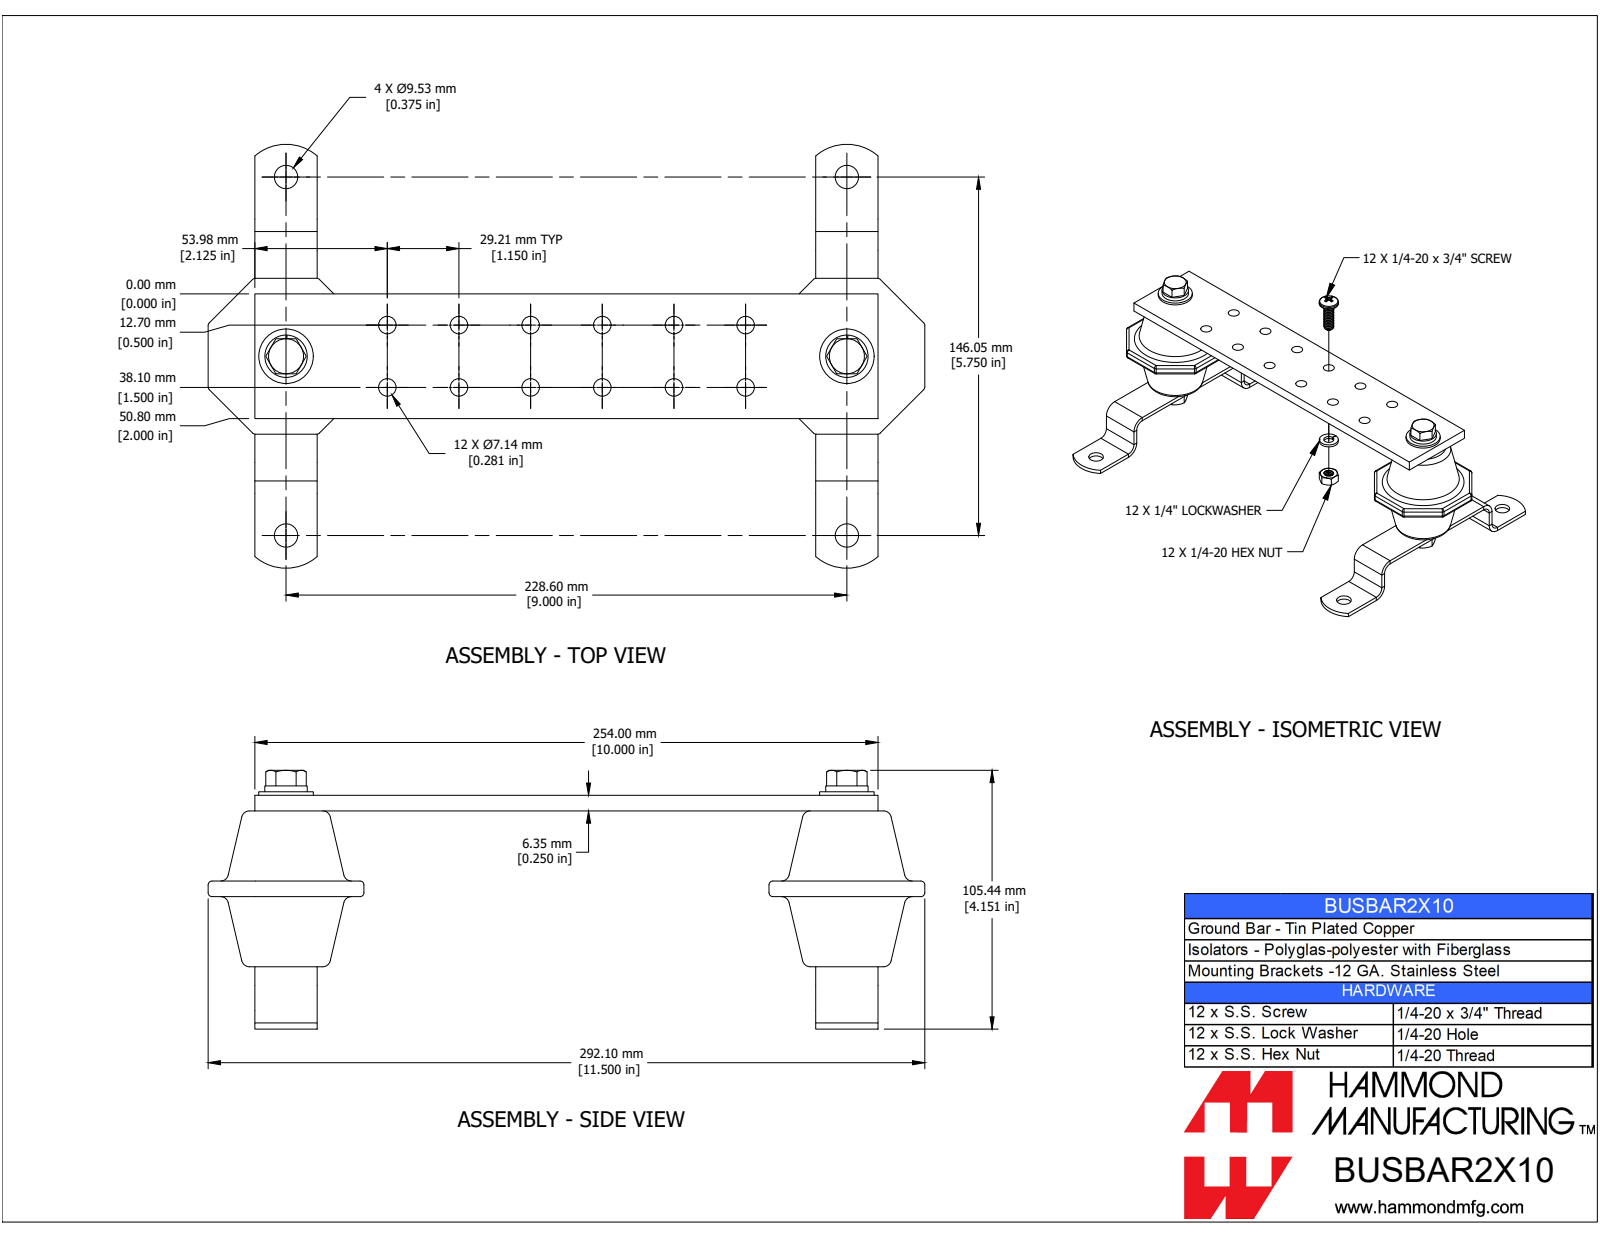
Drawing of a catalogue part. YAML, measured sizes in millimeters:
part_name: "BUSBAR2X10"
step_written_by: "SolidWorks 2019 (AUTOMOTIVE_DESIGN)"
units: millimeters
bodies: {solids: 5, faces: 330, planar: 134, cylindrical: 120, other: 76}
overall_size: [292.1, 172.7, 105.4]
volume: 308600
surface_area: 90130
round_holes:
  - {diameter: 7.1, count: 12}
  - {diameter: 9.5, count: 4}
  - {diameter: 7.8, count: 2}
  - {diameter: 10.3, count: 2}
  - {diameter: 12.7, count: 2}
  - {diameter: 14.3, count: 2}
  - {diameter: 9.8, count: 1}
  - {diameter: 9.8, count: 1}
round_bosses_or_shafts:
  - {diameter: 22.2, count: 2}
  - {diameter: 17.3, count: 2}
  - {diameter: 9.5, count: 2}
partial_cylinders:
  - {radius: 1.6, count: 32}
  - {radius: 1.6, count: 13}
  - {radius: 5.1, count: 4}
  - {radius: 7.6, count: 4}
  - {radius: 19.3, count: 4}
face_to_face_distances: [6.4, 2.5, 22.9, 25.4, 69.9, 63.5, 66, 72.4, 34.9, 88.9]
hole_center_spacings: [29.2, 38.7, 58.4, 63.7, 25.4, 87.6, 91.2, 71.6]
